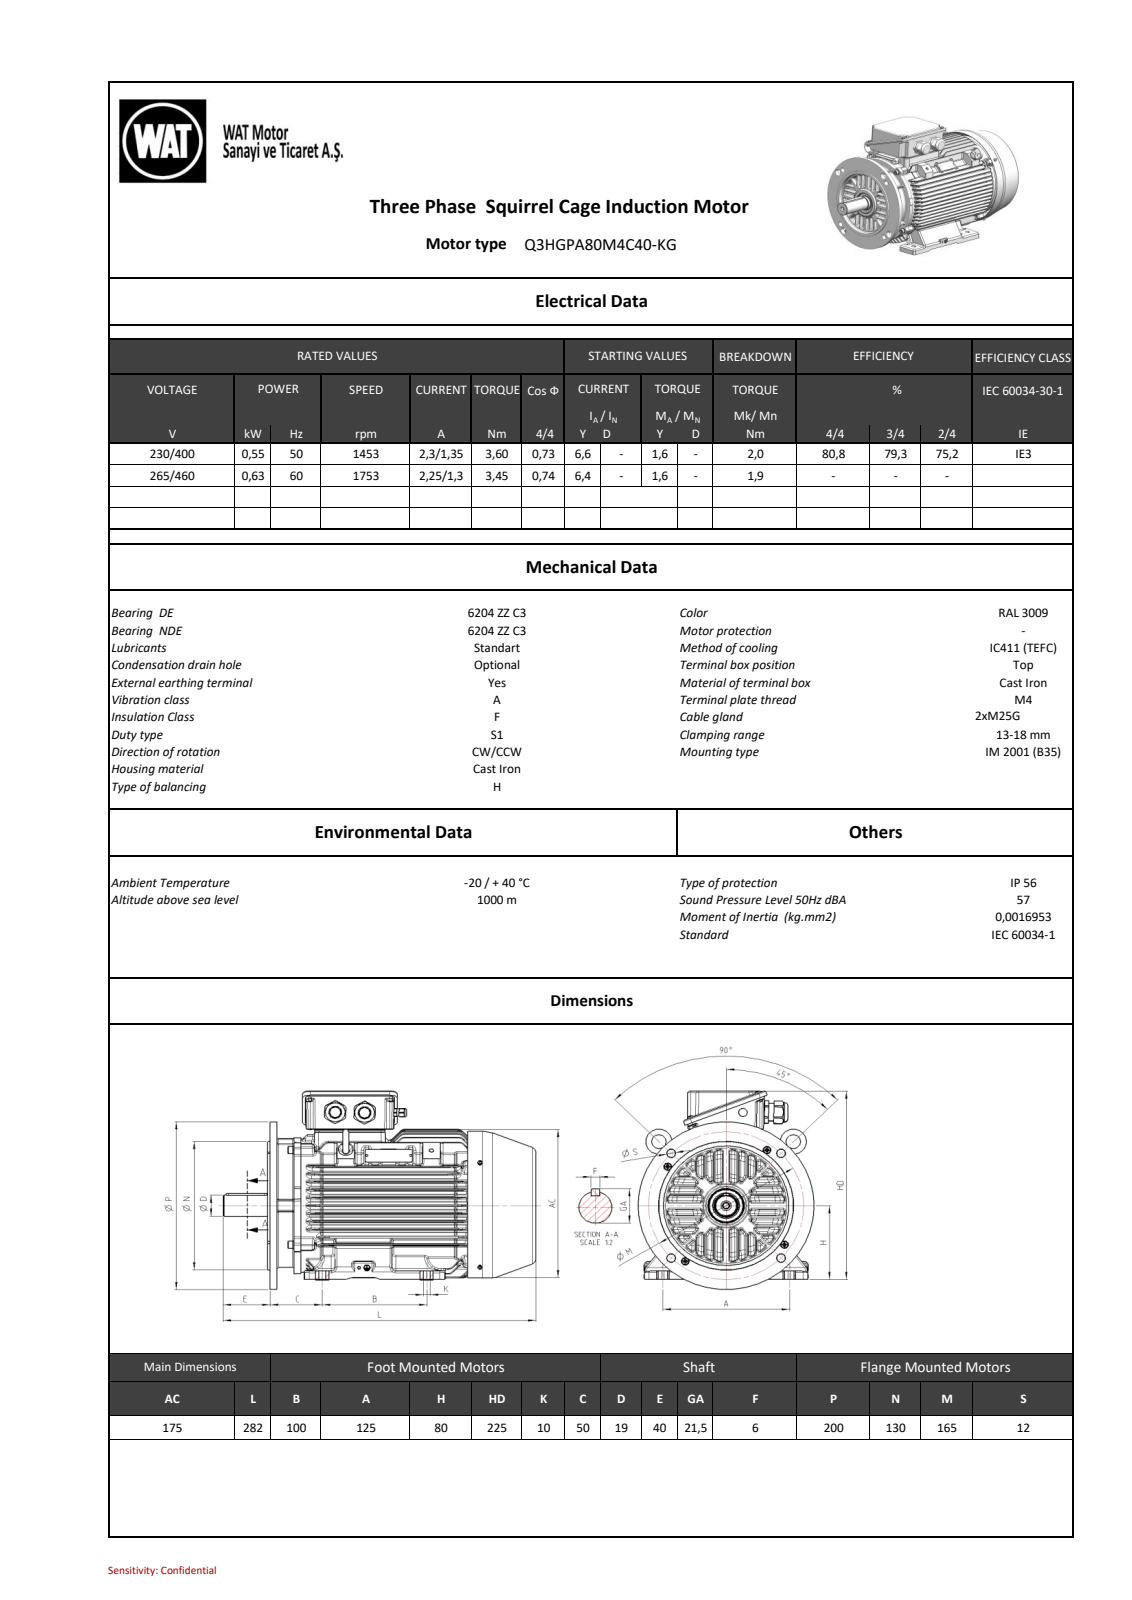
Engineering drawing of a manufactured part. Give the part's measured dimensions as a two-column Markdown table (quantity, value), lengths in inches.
| quantity | value |
| --- | --- |
| part name | 26000A30F4D8ro9n |
| STEP written by | SIEMENS PLM Software NX 11.0 (AUTOMOTIVE_DESIGN) |
| units | inches |
| bodies | 0 solids, 2949 faces (779 planar, 810 cylindrical, 1360 other) |
| overall size | 11.091 × 9.645 × 8.714 |
| round holes (diameter × count) | 0.394 × 6, 0.472 × 4, 0.098 × 2, 0.13 × 2, 0.677 × 2, 0.252 × 1, 0.256 × 1, 1.094 × 1, 1.102 × 1, 6.614 × 1 |
| round bosses / shafts (diameter × count) | 0.787 × 4, 0.341 × 3, 0.315 × 3, 0.197 × 3, 1.091 × 2, 0.994 × 2, 0.335 × 2, 7.874 × 1 |
| partial cylindrical surfaces (radius × count) | 0.059 × 309, 0.079 × 53, 0.098 × 40, 0.157 × 26, 0.039 × 24, 0.197 × 22, 0.276 × 13, 1.043 × 12 |
| main face-to-face distances | 0.195, 7.676, 7.871, 1.645, 9.321, 9.516, 2.463, 0.119, 0.059, 6.022 |
| hole center spacings | 4.593, 5.251, 0.848, 2.411, 3.031, 3.248, 3.826, 4.983 |
